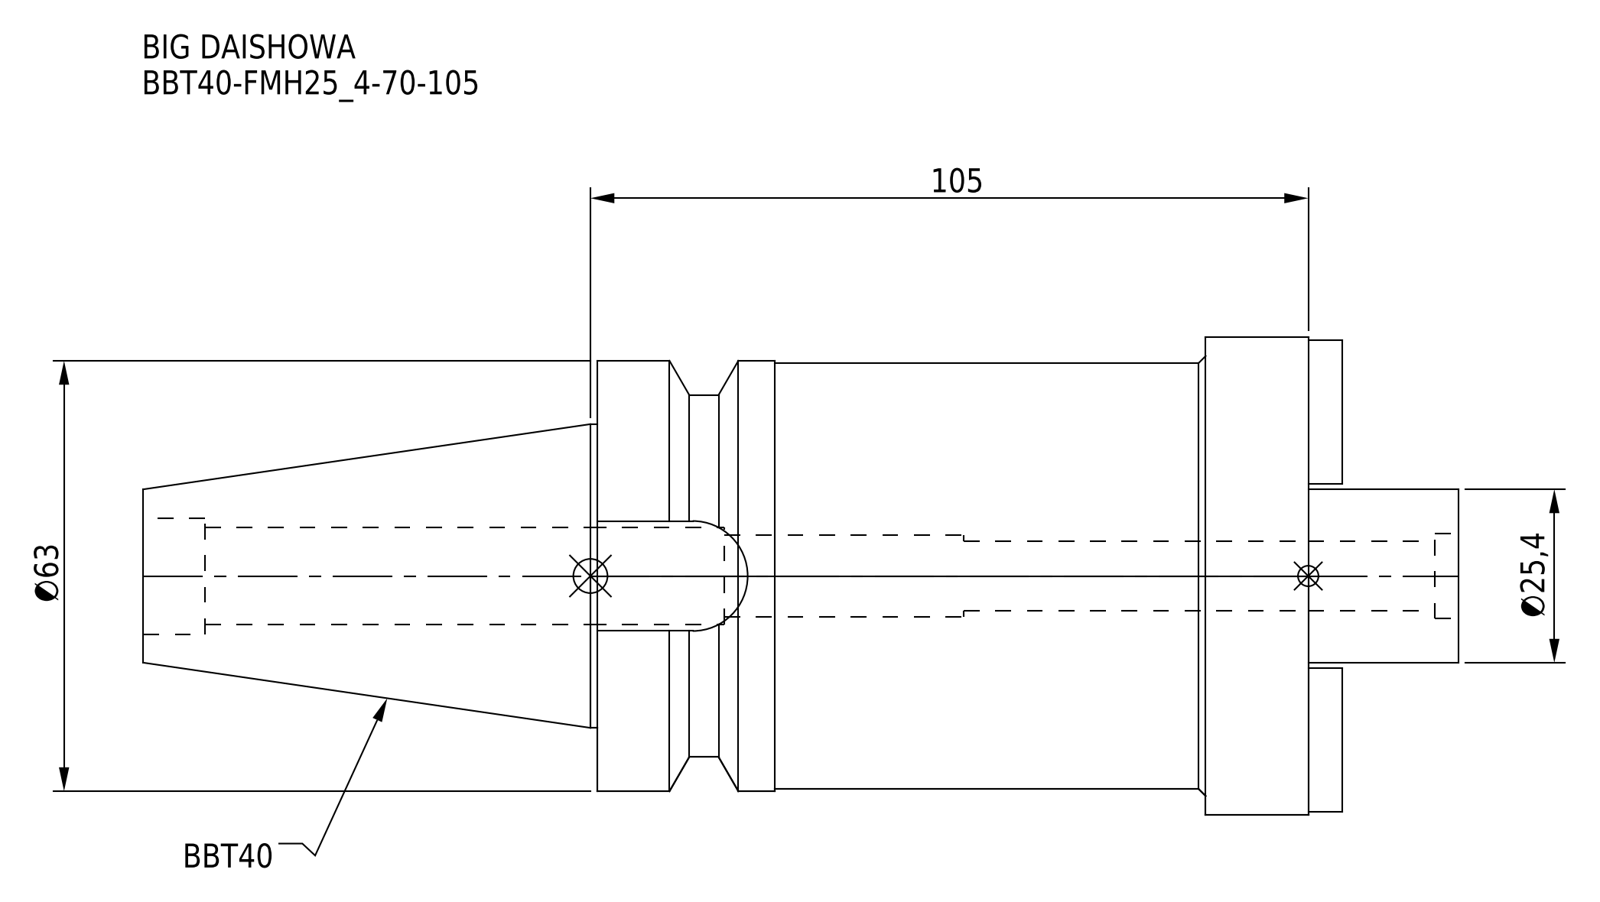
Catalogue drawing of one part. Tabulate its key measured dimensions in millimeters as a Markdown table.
| quantity | value |
| --- | --- |
| part name | BBT40-FMH25_4-70-105 |
| STEP written by | CREO PARAMETRIC BY PTC INC, 2016380 (AUTOMOTIVE_DESIGN) |
| units | millimeters |
| bodies | 1 solid, 64 faces (26 planar, 30 cylindrical, 8 other) |
| overall size | 192.4 × 70 × 70 |
| volume | 375 059 mm³ |
| surface area | 45 675 mm² |
| round holes (diameter × count) | 10.25 × 1, 12 × 1, 12.5 × 1, 14.2 × 1, 17 × 1 |
| round bosses / shafts (diameter × count) | 70 × 1, 63 × 1, 62.4 × 1, 53 × 1, 44.45 × 1, 25.4 × 1 |
| partial cylindrical surfaces (radius × count) | 8.05 × 1 |
| main face-to-face distances | 104, 15, 89, 17.75, 27.25, 5, 20, 109, 17, 22 |
